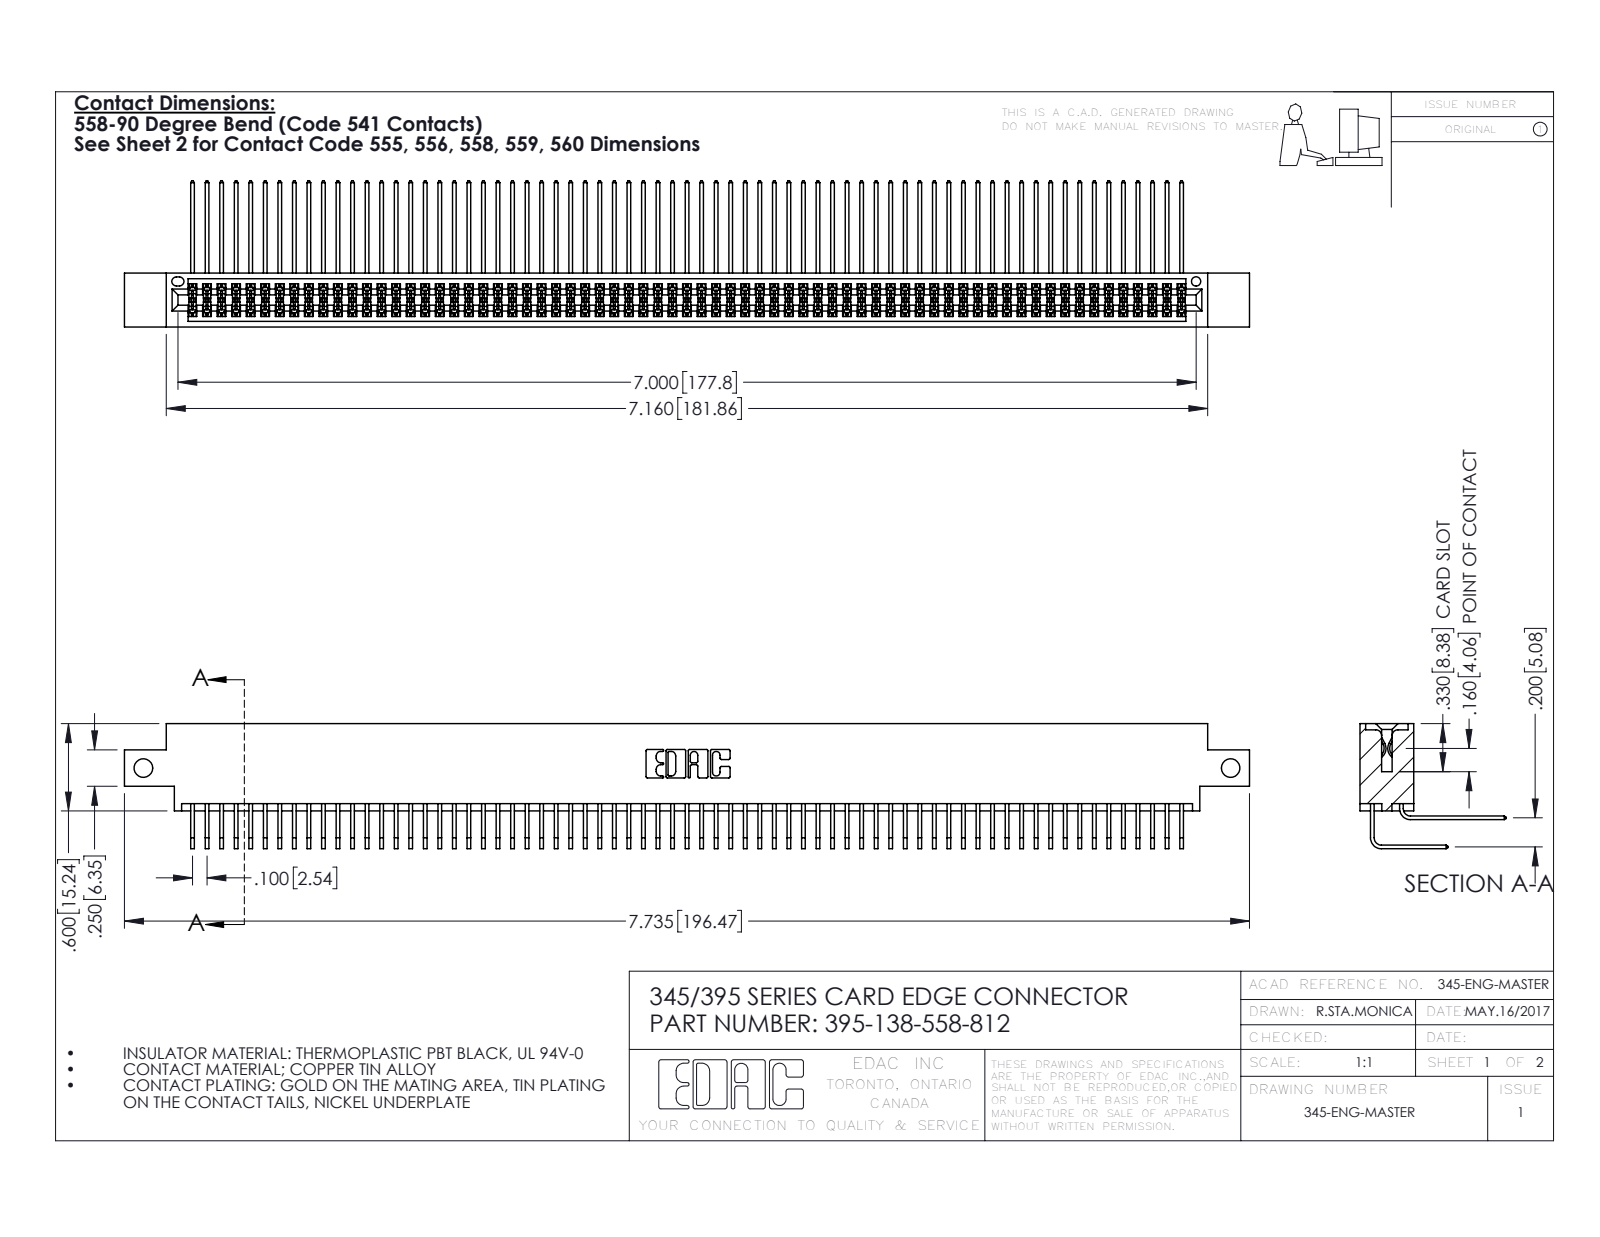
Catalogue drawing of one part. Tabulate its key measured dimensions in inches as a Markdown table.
| quantity | value |
| --- | --- |
| part name | 395-138-558-812; 345 Part_0.170 Offset - Side Mount; 345-292-001_558 Tail - 2; 345-292-001_558 559 Tail - 1 |
| STEP written by | SolidWorks 2016 (CONFIG_CONTROL_DESIGN) |
| units | inches |
| bodies | 139 solids, 7306 faces (4914 planar, 2392 cylindrical, 0 other) |
| overall size | 7.735 × 1.005 × 0.859 |
| volume | 1.216 in³ |
| surface area | 52.29 in² |
| round holes (diameter × count) | 0.128 × 2, 0.064 × 1 |
| partial cylindrical surfaces (radius × count) | 0.006 × 275, 0.01 × 22, 0.007 × 6, 0.031 × 6, 0.026 × 3, 0.014 × 2, 0.019 × 2, 0.022 × 2 |
| main face-to-face distances | 0.072, 0.298, 0.2, 0.37, 0.098, 0.272, 0.025, 0.225, 0.175, 0.025 |
| hole center spacings | 7.475 |
